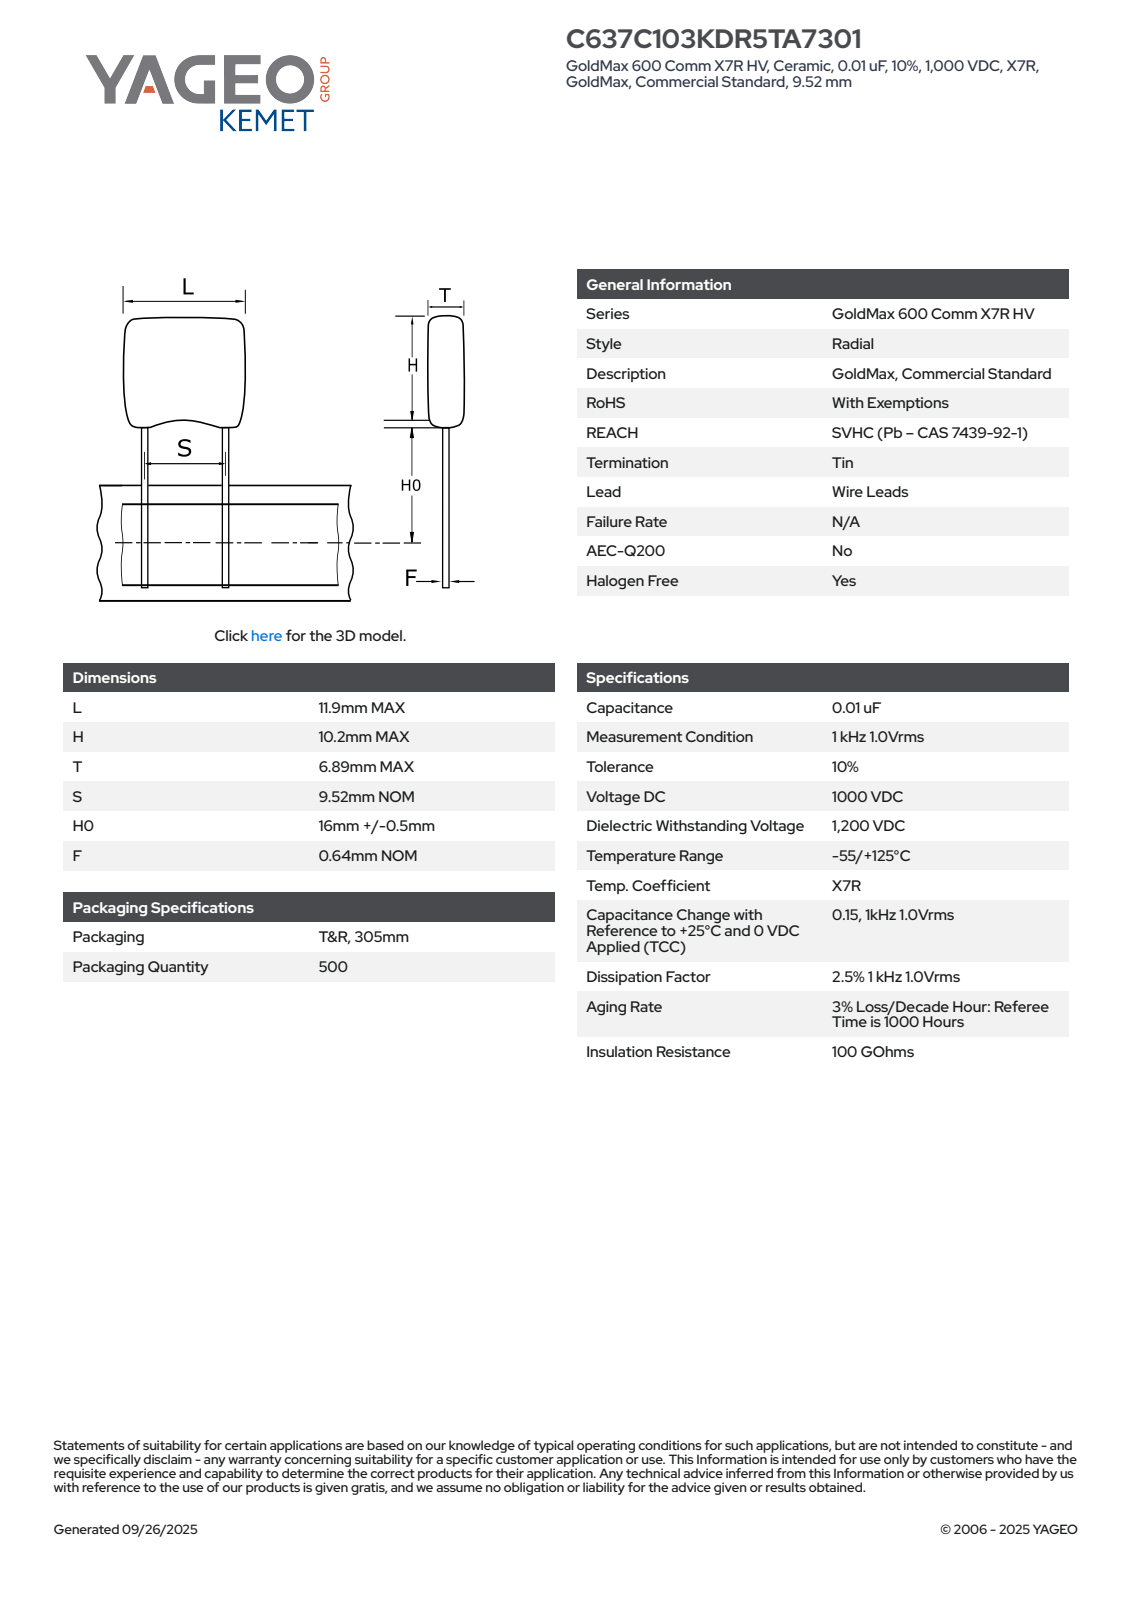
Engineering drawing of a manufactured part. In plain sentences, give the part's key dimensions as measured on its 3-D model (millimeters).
The part is named "CCR_KRCST_11.9X10.2_L11.9H10.2T6.89S9.52H016.5F0.64". Its 3-D file was written by "SolidWorks 2014 (AUTOMOTIVE_DESIGN)". It is 4 solids with 83 faces: 65 planar, 14 cylindrical and 4 other. Overall it measures 27.86 by 11.9 by 6.89 millimeters. Its volume is 930 cubic millimeters and its surface area 632 square millimeters. Round bosses or shafts: 2 of diameter 0.64. Partial cylindrical surfaces (rounded edges, fillets, slot ends): 10 of radius 0.75. The main face-to-face distances are 6.89, 11.9, 11.36, 16.5, 27.86, 5.05, 6.31, 22.81, 21.55, 1.26.
